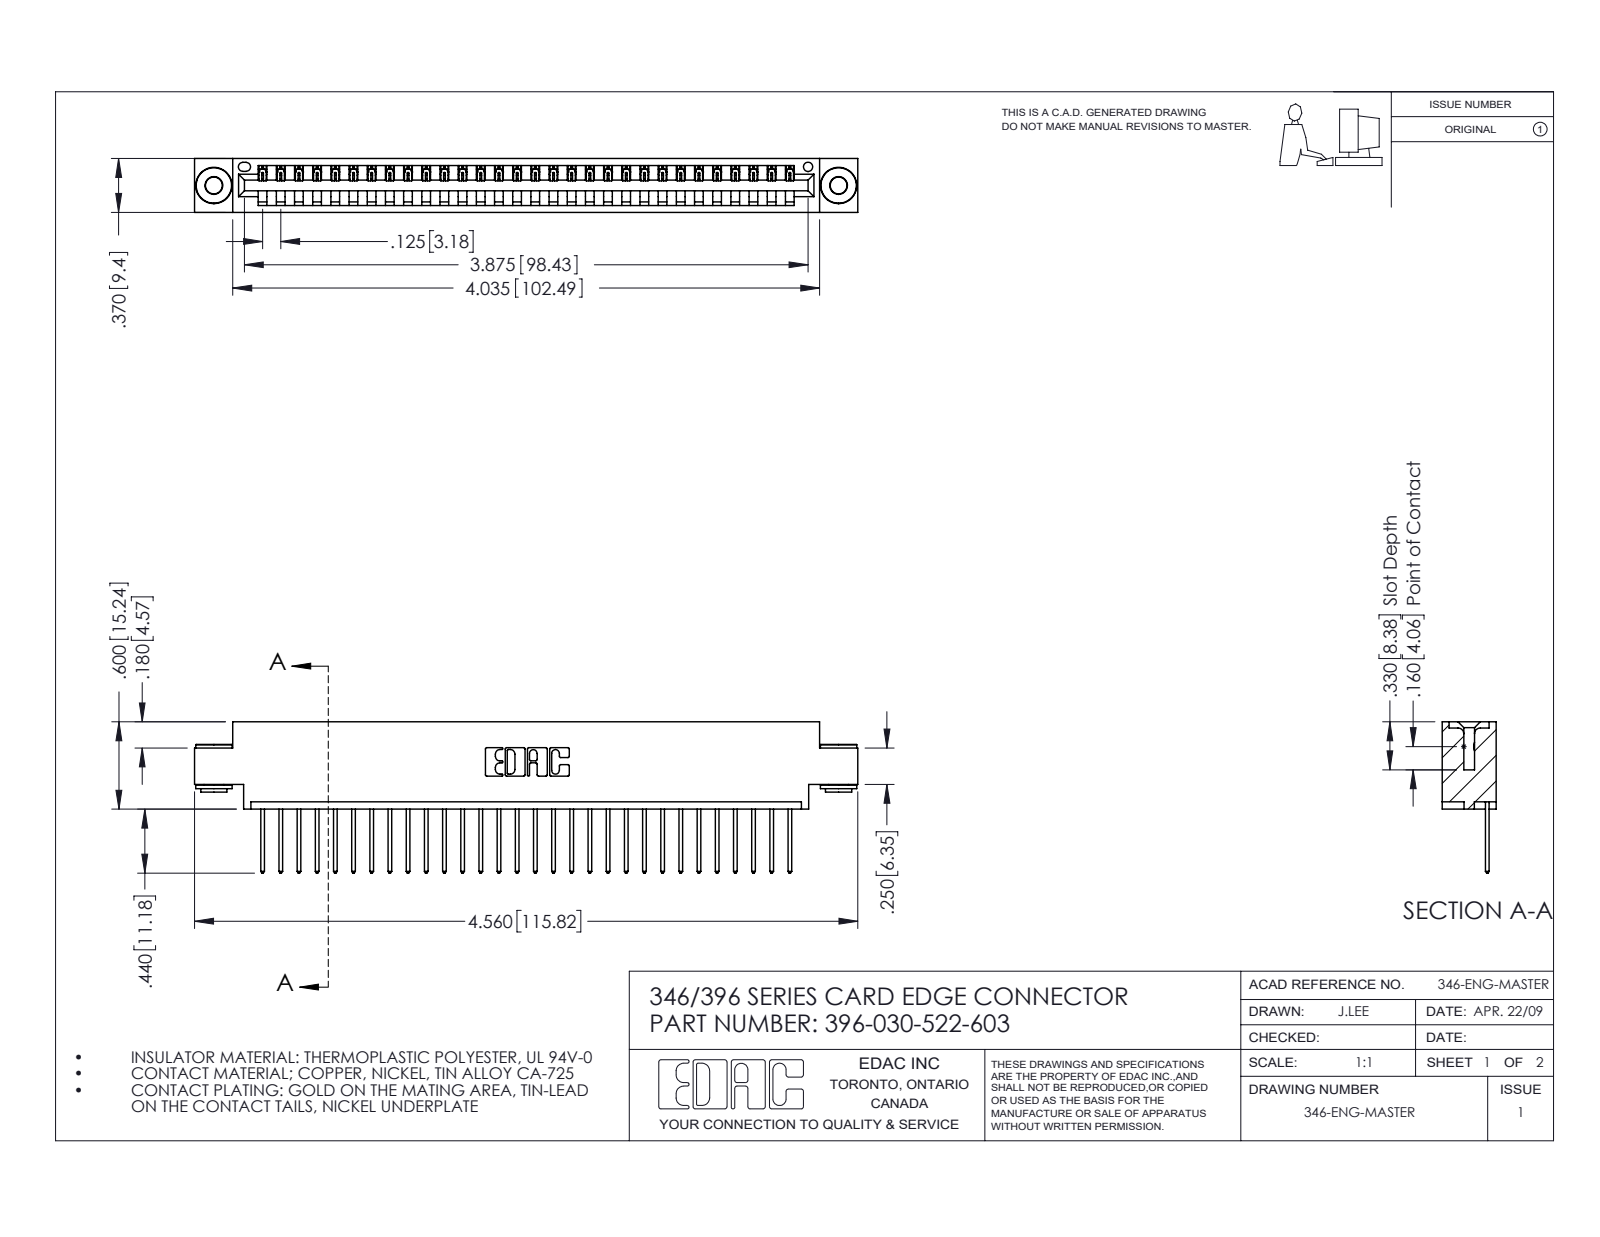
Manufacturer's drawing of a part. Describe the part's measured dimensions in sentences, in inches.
The part is named "345-292-001_345-293-122; 396-030-522-603; 345-250-002_345-250-002-102; 346 Part_0.170 Offset - 0.156 Dia-TH". Its 3-D file was written by "SolidWorks 2016 (CONFIG_CONTROL_DESIGN)". It is 33 solids with 1904 faces: 1290 planar, 606 cylindrical and 8 other. Overall it measures 4.56 by 1.04 by 0.37 inches. Its volume is 0.663 cubic inches and its surface area 21.62 square inches. Round holes: 2 of diameter 0.116, 2 of diameter 0.156, 1 of diameter 0.064. Round bosses or shafts: 2 of diameter 0.25, 2 of diameter 0.18, 2 of diameter 0.136. Partial cylindrical surfaces (rounded edges, fillets, slot ends): 60 of radius 0.006, 60 of radius 0.01, 22 of radius 0.01, 6 of radius 0.007, 6 of radius 0.031, 3 of radius 0.026, 2 of radius 0.031, 2 of radius 0.04. The main face-to-face distances are 0.048, 0.322, 0.37, 0.25, 0.025, 0.072, 0.298, 0.148, 0.222, 0.1. The hole center spacings are 0.246, 4.087, 4.295.
